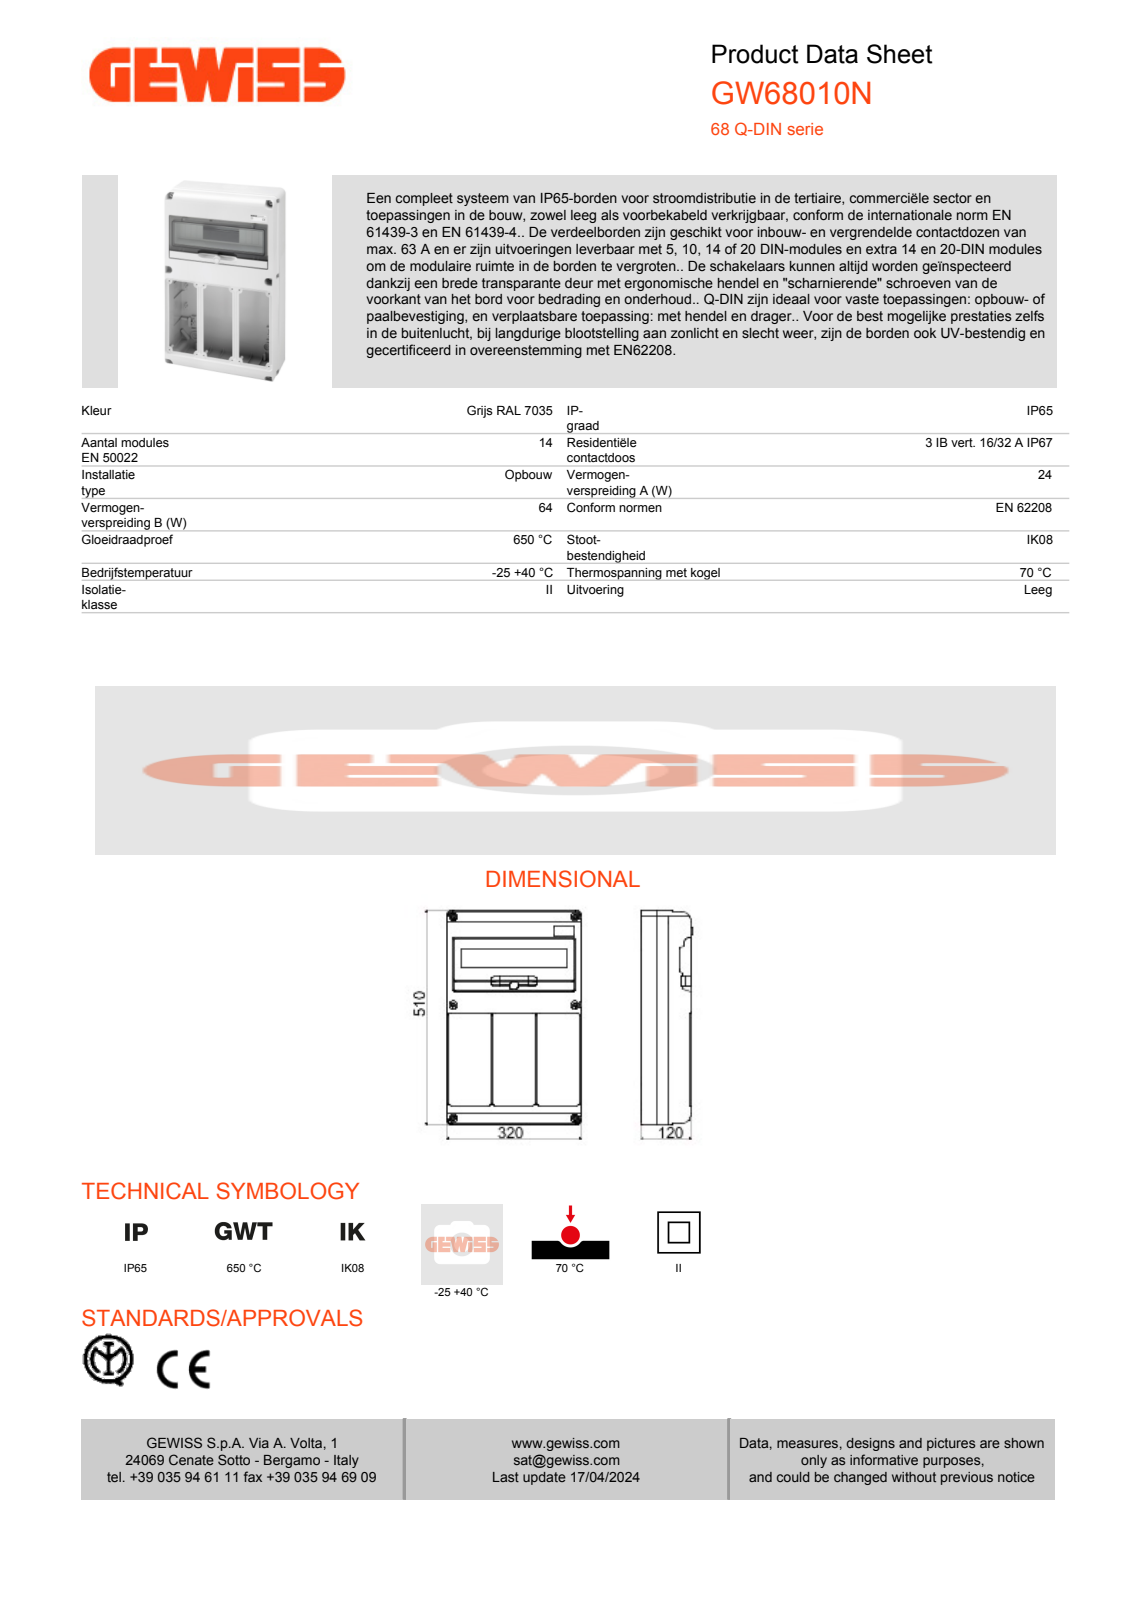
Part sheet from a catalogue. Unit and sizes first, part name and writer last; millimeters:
Units: millimetres
Overall size (bounding box): 510 × 320 × 126.04
Round bosses / shafts (diameter × count): ⌀6.9 ×16, ⌀6.5 ×4
Partial cylindrical surfaces — rounded edges, fillets, slot ends (radius × count): R2 ×60, R3.5 ×22, R0.5 ×15, R1.5 ×14, R1.7 ×12, R9 ×12, R0.3 ×10, R4 ×10
Main face-to-face distances: 3, 115.3, 118.3, 313.72, 6.5, 309.65, 4.07, 320, 112.3, 103.5
Volume: 2 984 000 mm³ · Surface area: 1 097 000 mm²
Bodies: 2 solids, 1414 faces (750 planar, 278 cylindrical, 386 other)
Part name (STEP PRODUCT): 55523476FXXX_FRON_14M_2A_GRAND; 55523450_FONDO_14_MOD_2_GRANDEZ; GW68010N_ASM
STEP written by: CREO PARAMETRIC BY PTC INC, 2020074 (CONFIG_CONTROL_DESIGN)
